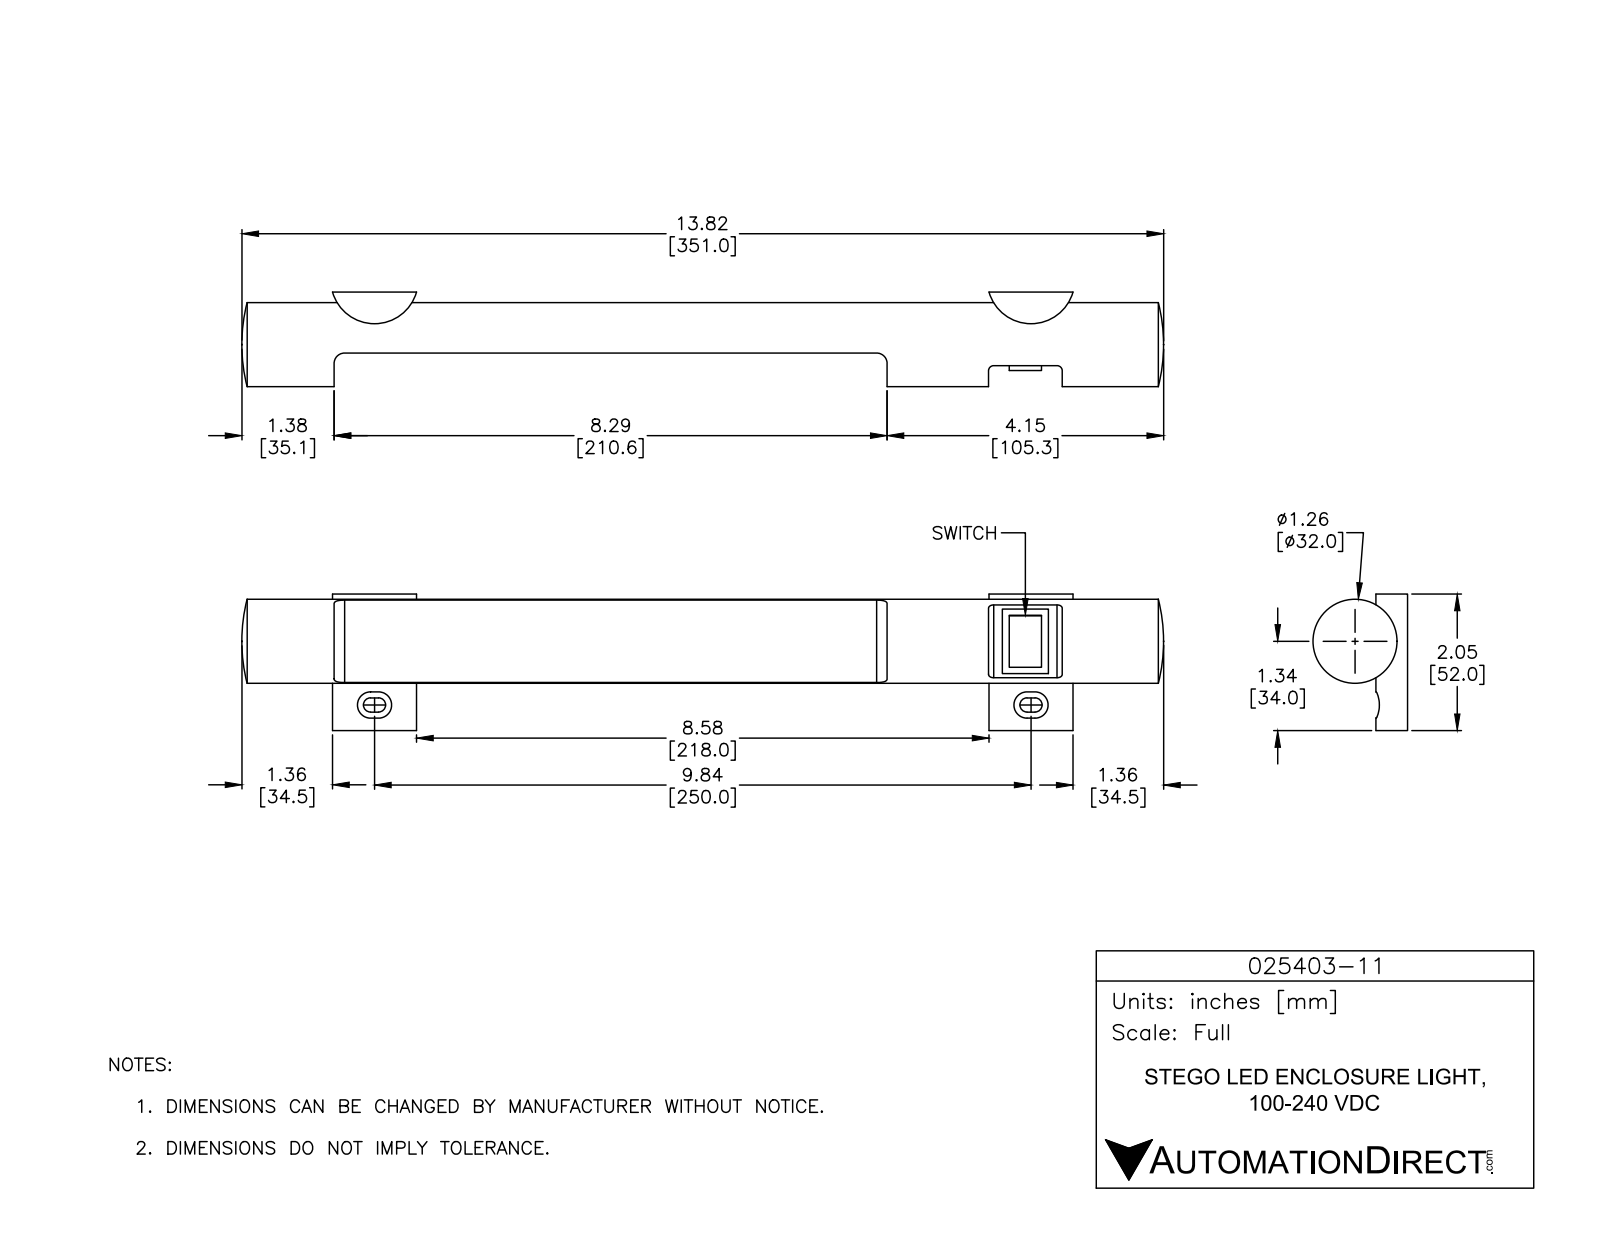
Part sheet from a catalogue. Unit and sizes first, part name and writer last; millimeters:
Units: millimetres
Overall size (bounding box): 351 × 52 × 36
Round bosses / shafts (diameter × count): ⌀32 ×1
Partial cylindrical surfaces — rounded edges, fillets, slot ends (radius × count): R2.7 ×4, R5 ×4, R2 ×2, R4 ×2, R16.64 ×2, R49.14 ×1
Main face-to-face distances: 23.2, 52, 28, 4.8, 27.36, 4.16, 0.64, 210.6, 2, 21.2
Volume: 234 750 mm³ · Surface area: 41 126 mm²
Bodies: 1 solid, 53 faces (31 planar, 18 cylindrical, 4 other)
Part name (STEP PRODUCT): PRODUCT_NAME_1
STEP written by: ACIS (CONFIG_CONTROL_DESIGN)
